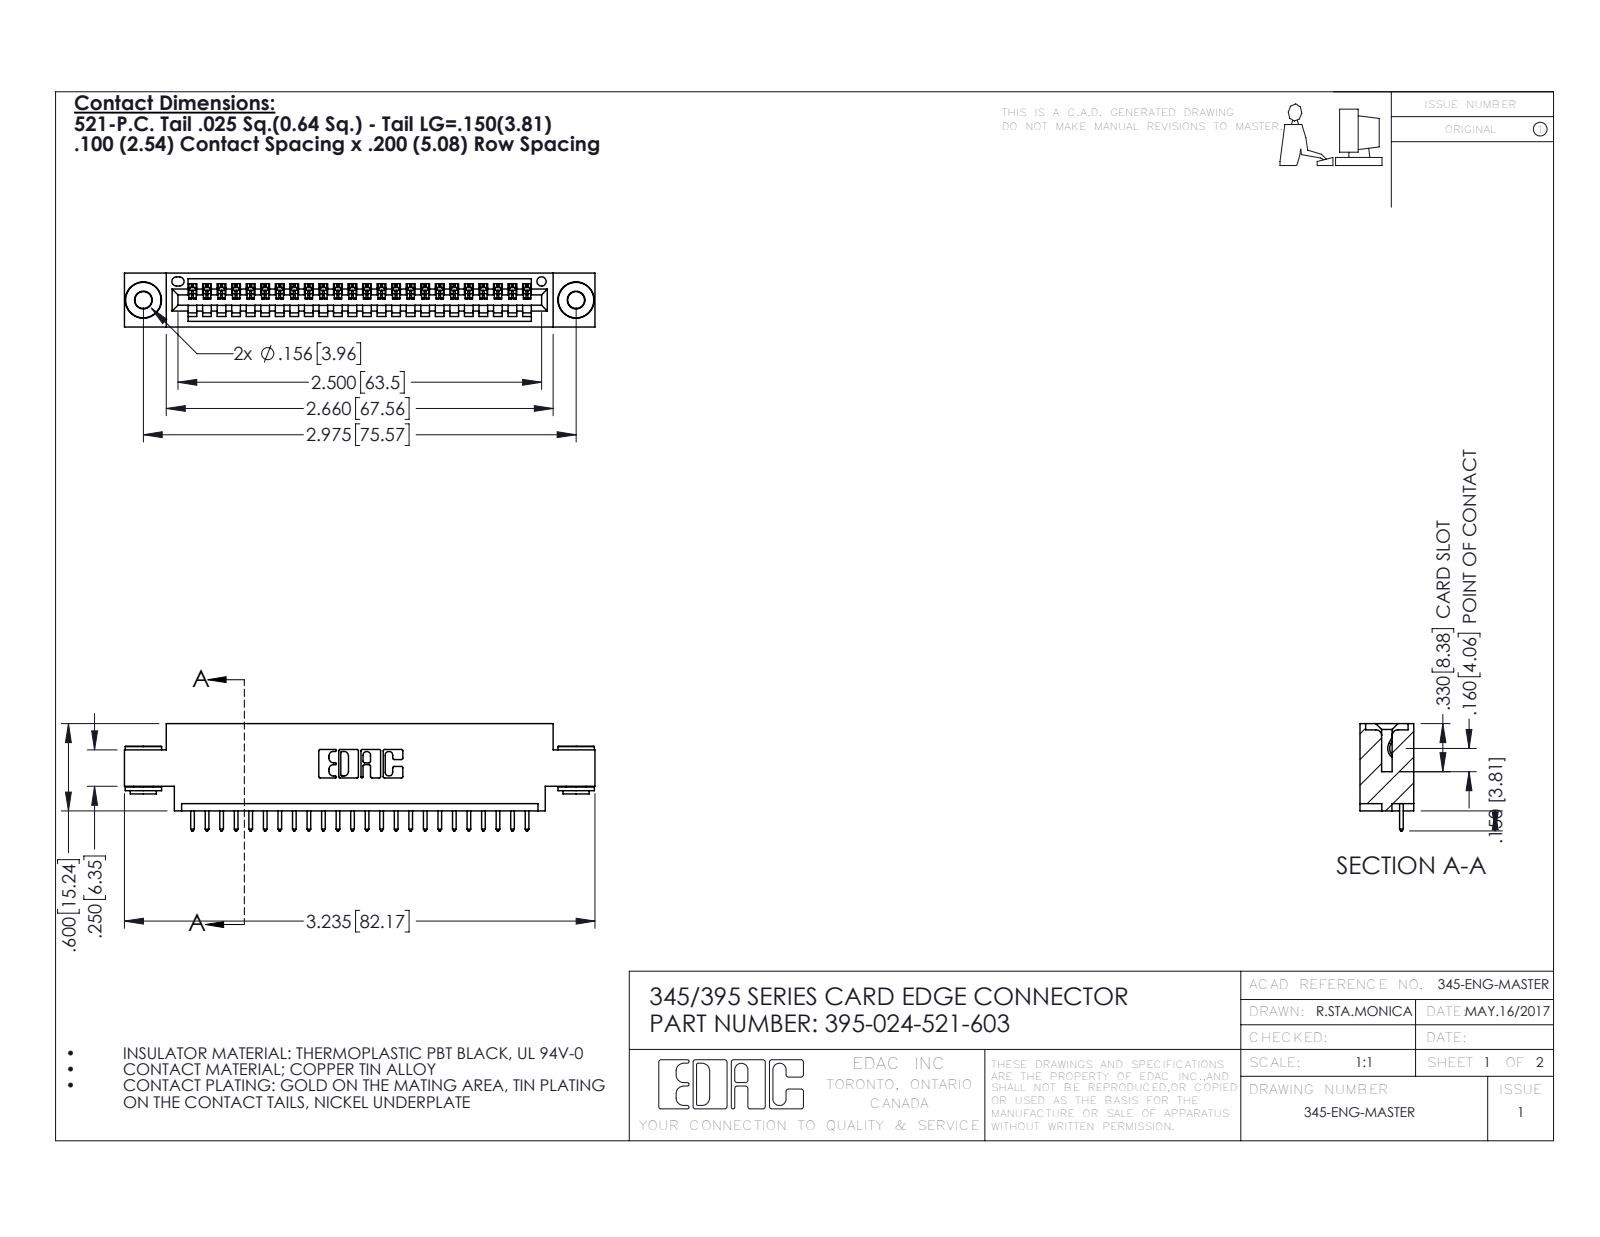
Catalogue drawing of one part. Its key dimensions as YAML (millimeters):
part_name: "345-250-002_345-250-002-102; 395-024-521-603; 345-292-001_345-293-121; 345 Part_0.170 Offset - 0.156 Dia-TH"
step_written_by: "SolidWorks 2016 (CONFIG_CONTROL_DESIGN)"
units: millimeters
bodies: {solids: 27, faces: 1560, planar: 1054, cylindrical: 498, other: 8}
overall_size: [82.2, 18.7, 9.4]
volume: 7490
surface_area: 9787
round_holes:
  - {diameter: 2.9, count: 2}
  - {diameter: 4, count: 2}
  - {diameter: 1.6, count: 1}
round_bosses_or_shafts:
  - {diameter: 6.4, count: 2}
  - {diameter: 4.6, count: 2}
  - {diameter: 3.5, count: 2}
partial_cylinders:
  - {radius: 0.2, count: 48}
  - {radius: 0.3, count: 48}
  - {radius: 0.3, count: 22}
  - {radius: 0.2, count: 6}
  - {radius: 0.8, count: 6}
  - {radius: 0.7, count: 3}
  - {radius: 0.8, count: 2}
  - {radius: 1, count: 2}
face_to_face_distances: [1.8, 7.6, 9.4, 5.1, 2.5, 6.9, 0.6, 5.7, 4.4, 3.8]
hole_center_spacings: [6.9, 69.6, 75.6]
